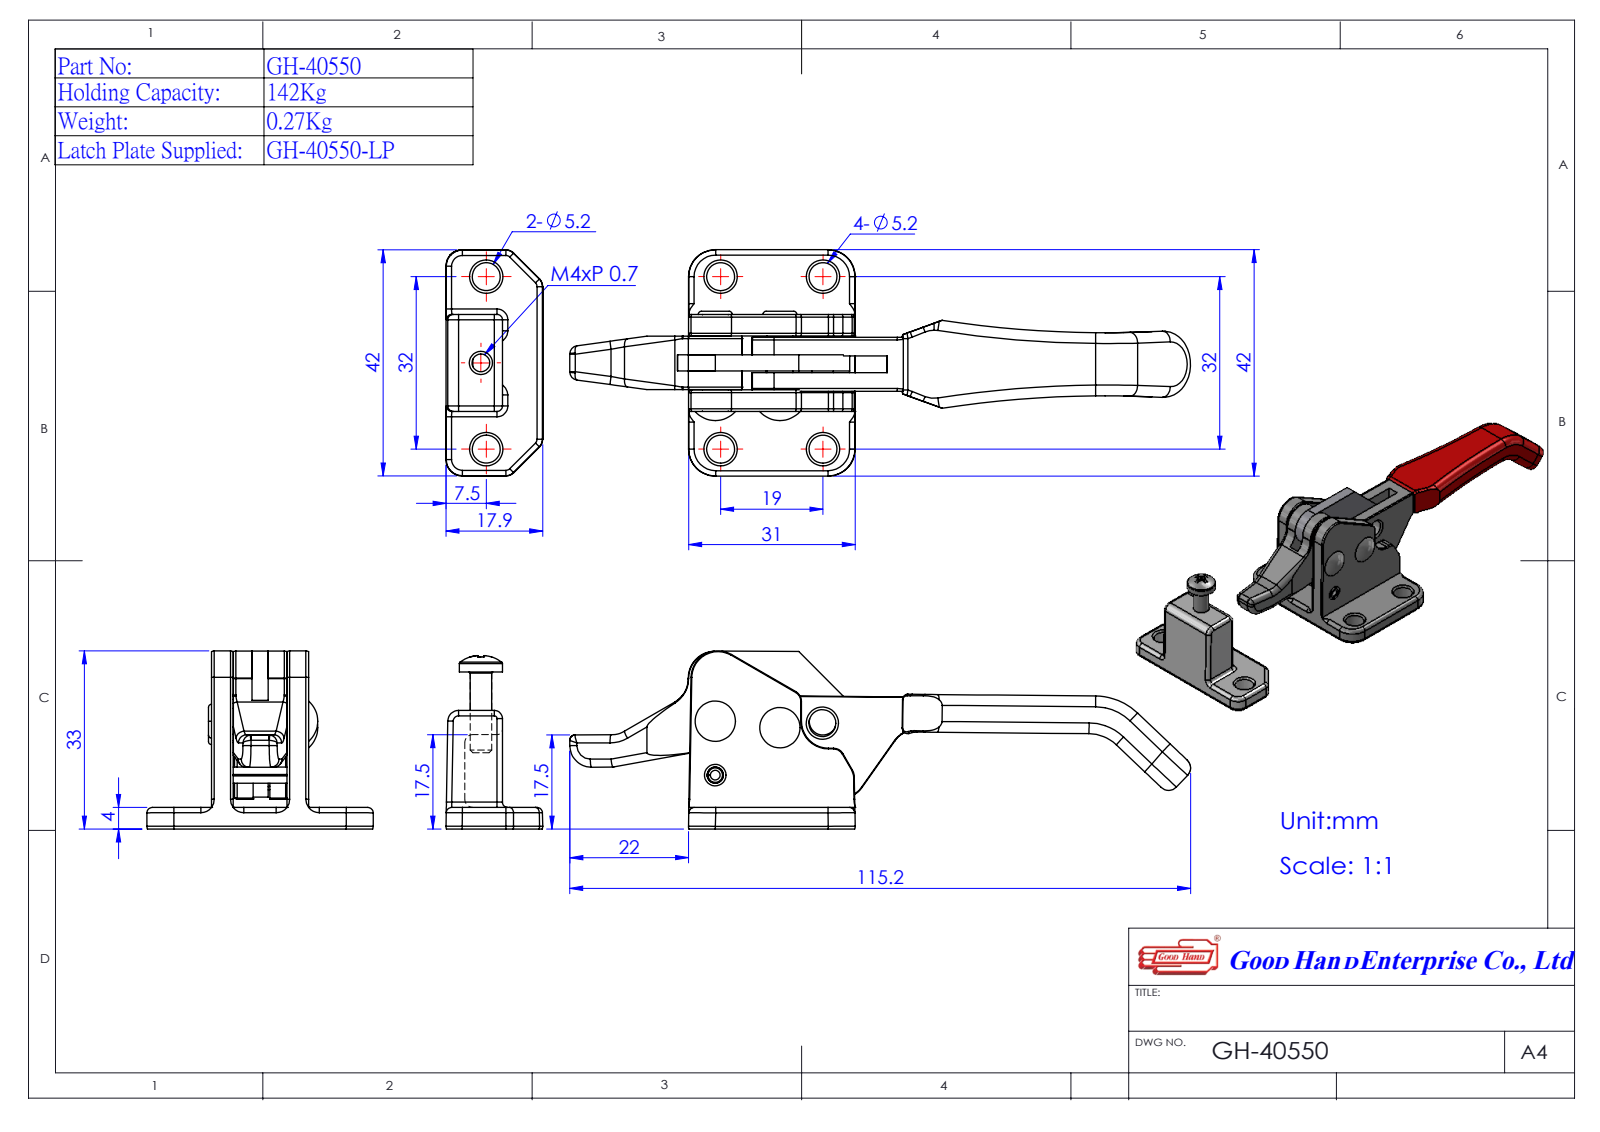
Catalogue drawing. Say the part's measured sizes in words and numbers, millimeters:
The part is named "GH-40550(簡化); Group3^GH-40550(簡化); Group6^GH-40550(簡化); 14050005-1^GH-40550(簡化) (+2 more)". Its 3-D file was written by "SolidWorks 2016 (AUTOMOTIVE_DESIGN)". It is 7 solids with 863 faces: 316 planar, 203 cylindrical and 344 other. Overall it measures 153.33 by 42 by 34.12 millimeters. Its volume is 19 115 cubic millimeters and its surface area 21 417 square millimeters. Round holes: 6 of diameter 5.2, 4 of diameter 3, 2 of diameter 5, 1 of diameter 1.07, 1 of diameter 3.3. Round bosses or shafts: 2 of diameter 3, 1 of diameter 8, 1 of diameter 4, 1 of diameter 1.03. Partial cylindrical surfaces (rounded edges, fillets, slot ends): 39 of radius 1.5, 29 of radius 1, 13 of radius 5, 6 of radius 2, 3 of radius 0.41, 3 of radius 0.43, 2 of radius 3, 2 of radius 4. The main face-to-face distances are 4, 14, 7.5, 10.5, 6.5, 3.5, 3.45, 10, 0.5, 18. The hole center spacings are 32, 9, 16.03, 19, 37.22, 58.5, 61.61, 66.68.
